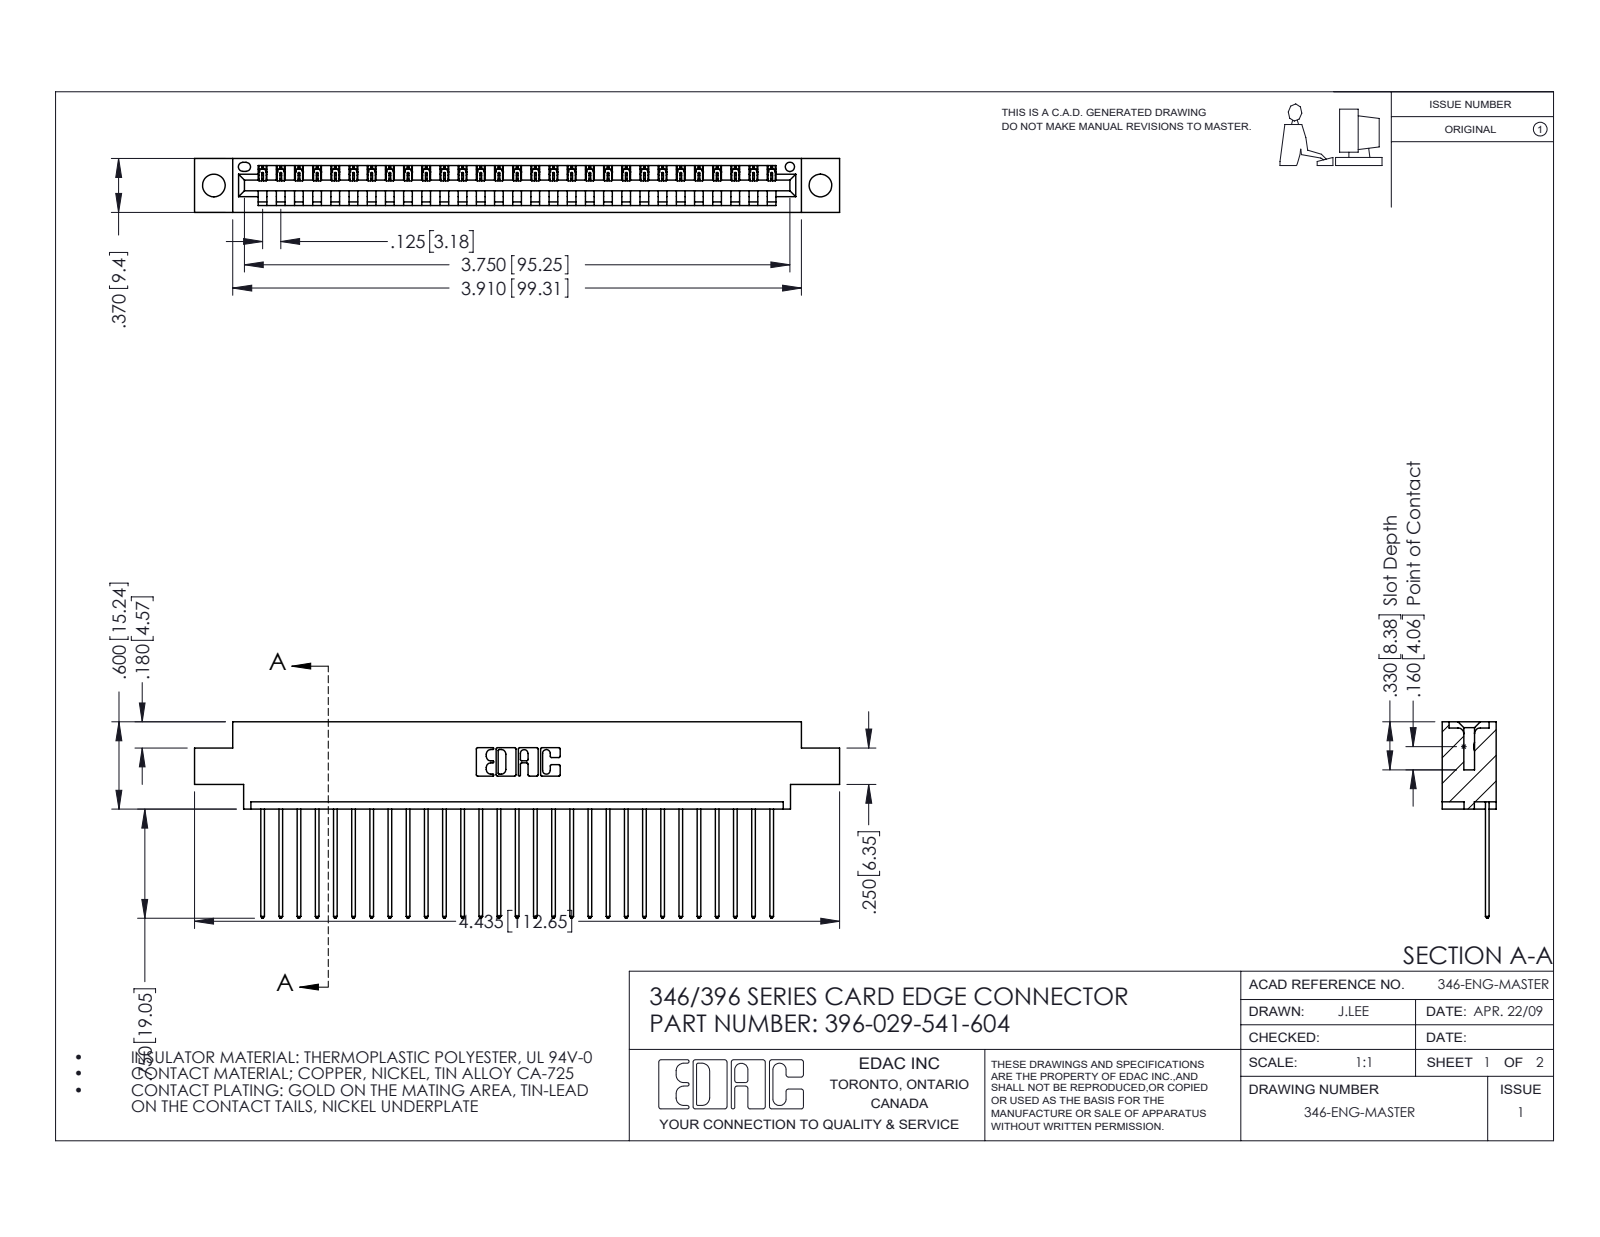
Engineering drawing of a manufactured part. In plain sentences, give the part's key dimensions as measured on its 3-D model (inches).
The part is named "396-029-541-604; 346 Part_0.170 Offset - 0.156 Dia-TH; 345-292-001_345-293-141". Its 3-D file was written by "SolidWorks 2016 (CONFIG_CONTROL_DESIGN)". It is 30 solids with 1808 faces: 1240 planar, 568 cylindrical and 0 other. Overall it measures 4.435 by 1.35 by 0.37 inches. Its volume is 0.644 cubic inches and its surface area 21.05 square inches. Round holes: 2 of diameter 0.156, 1 of diameter 0.064. Partial cylindrical surfaces (rounded edges, fillets, slot ends): 58 of radius 0.006, 58 of radius 0.01, 22 of radius 0.01, 6 of radius 0.007, 6 of radius 0.031, 3 of radius 0.026, 2 of radius 0.031, 2 of radius 0.04. The main face-to-face distances are 0.048, 0.322, 0.37, 0.25, 0.072, 0.298, 0.025, 0.148, 0.222, 0.1. The hole center spacings are 0.246, 3.962, 4.17.
